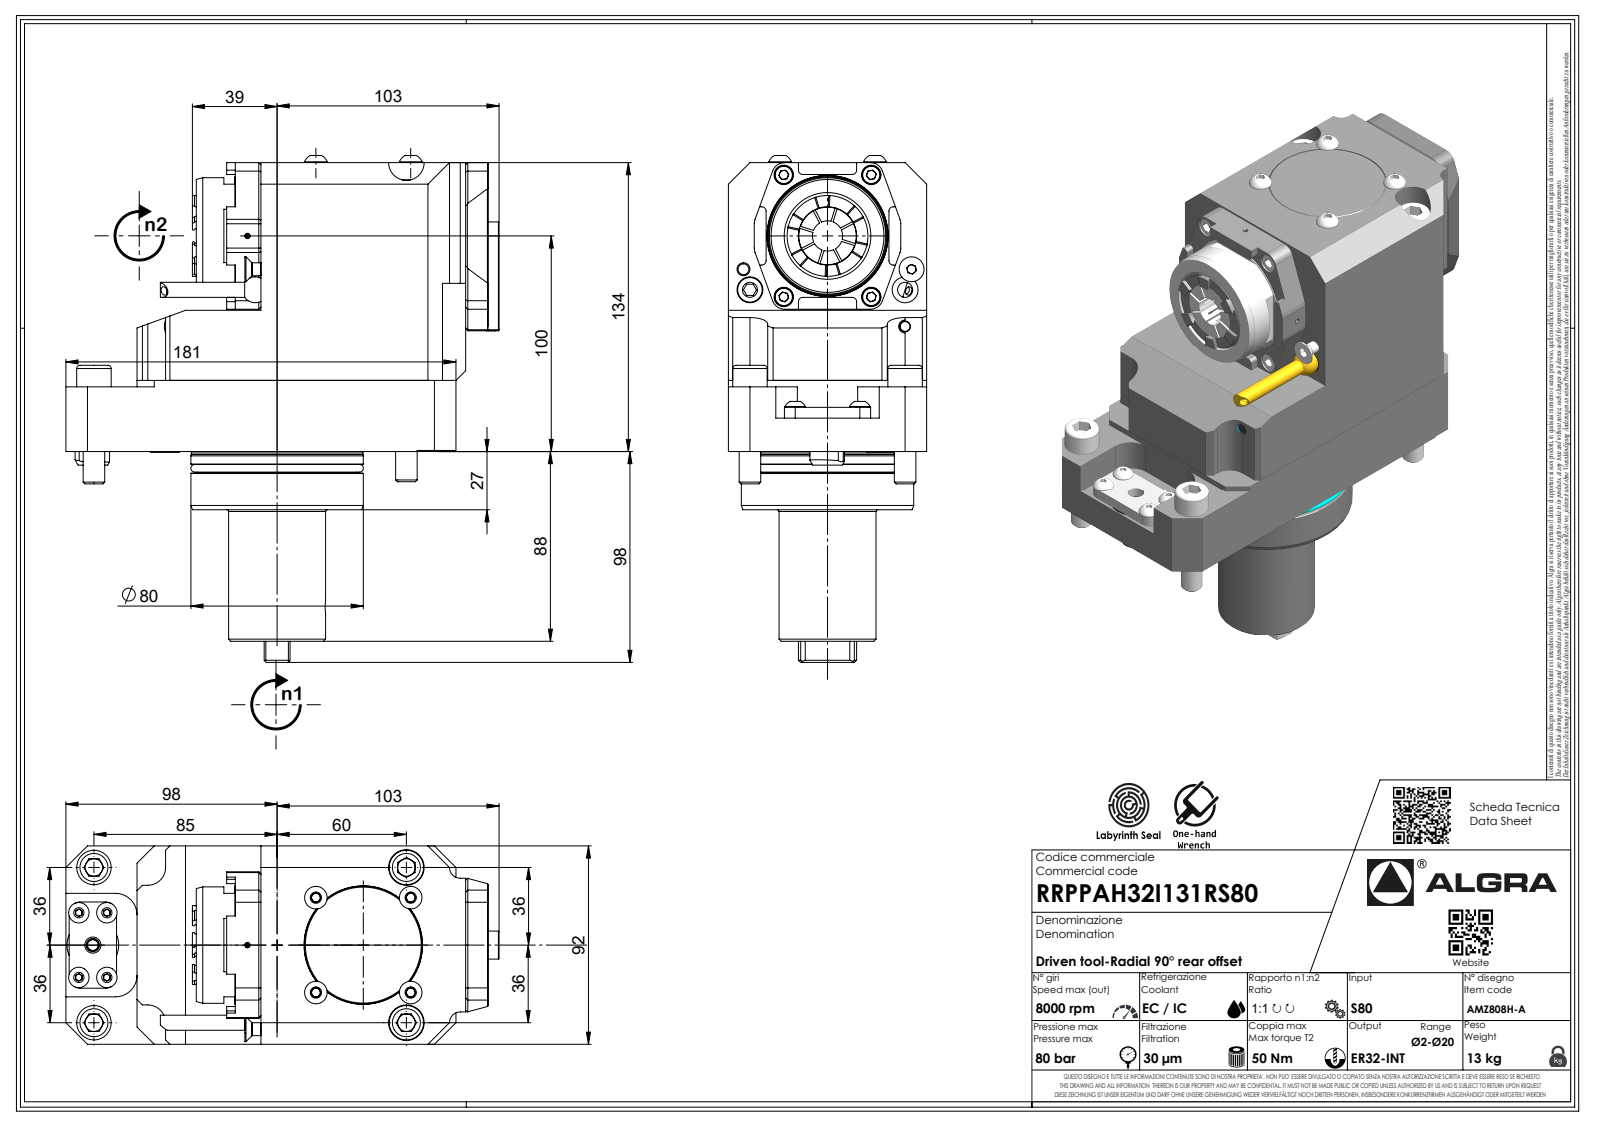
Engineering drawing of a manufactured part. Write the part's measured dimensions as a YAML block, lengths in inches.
part_name: "RRPPAH32I121RS80"
step_written_by: "SolidWorks 2023 (AUTOMOTIVE_DESIGN)"
units: inches
bodies: {solids: 1, faces: 609, planar: 375, cylindrical: 81, other: 153}
overall_size: [9.126, 7.717, 3.622]
volume: 114.5
surface_area: 183.8
round_holes:
  - {diameter: 0.083, count: 1}
round_bosses_or_shafts:
  - {diameter: 3.15, count: 1}
  - {diameter: 3.134, count: 1}
  - {diameter: 2.898, count: 1}
  - {diameter: 2.126, count: 1}
  - {diameter: 1.772, count: 1}
  - {diameter: 0.63, count: 1}
  - {diameter: 0.251, count: 1}
  - {diameter: 0.067, count: 1}
partial_cylinders:
  - {radius: 0.079, count: 8}
  - {radius: 0.236, count: 8}
  - {radius: 0.013, count: 7}
  - {radius: 0.02, count: 7}
  - {radius: 0.146, count: 7}
  - {radius: 0.197, count: 6}
  - {radius: 0.325, count: 4}
  - {radius: 0.394, count: 2}
face_to_face_distances: [3.622, 5.276, 2.697, 2.579, 3.563, 1.181, 0.591, 1.063, 3.642, 6.339]
